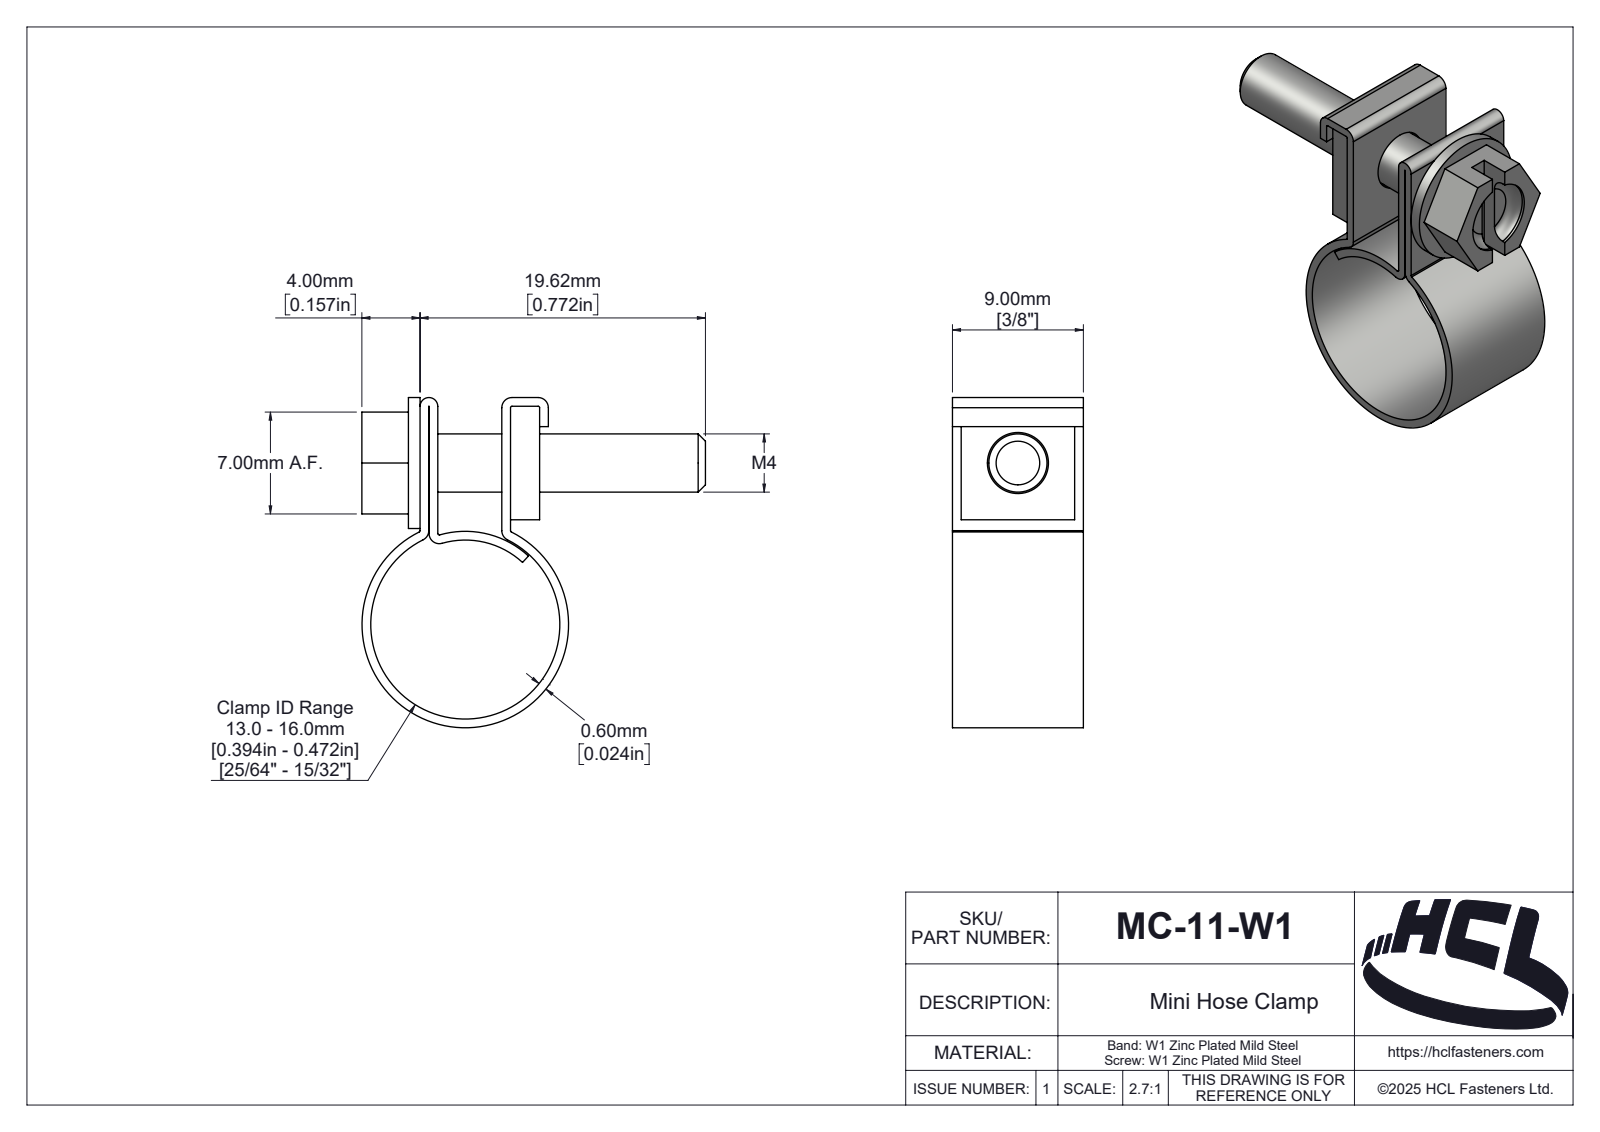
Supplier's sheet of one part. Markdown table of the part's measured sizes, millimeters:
| quantity | value |
| --- | --- |
| part name | MC-11-W1 |
| STEP written by | SolidWorks 2025 (AUTOMOTIVE_DESIGN) |
| units | millimeters |
| bodies | 3 solids, 175 faces (38 planar, 84 cylindrical, 53 other) |
| overall size | 23.62 × 22.69 × 9 |
| volume | 879 mm³ |
| surface area | 2 077 mm² |
| round holes (diameter × count) | 4.2 × 1, 5 × 1, 13 × 1 |
| round bosses / shafts (diameter × count) | 14.2 × 1, 9 × 1, 4 × 1 |
| partial cylindrical surfaces (radius × count) | 0.1 × 5, 0.7 × 5, 0.2 × 1, 0.61 × 1, 0.81 × 1, 1.01 × 1, 1.06 × 1, 1.28 × 1 |
| main face-to-face distances | 0.6, 0.62, 5, 5.62, 6.22, 7, 2, 2.6, 8.22, 7.6 |
